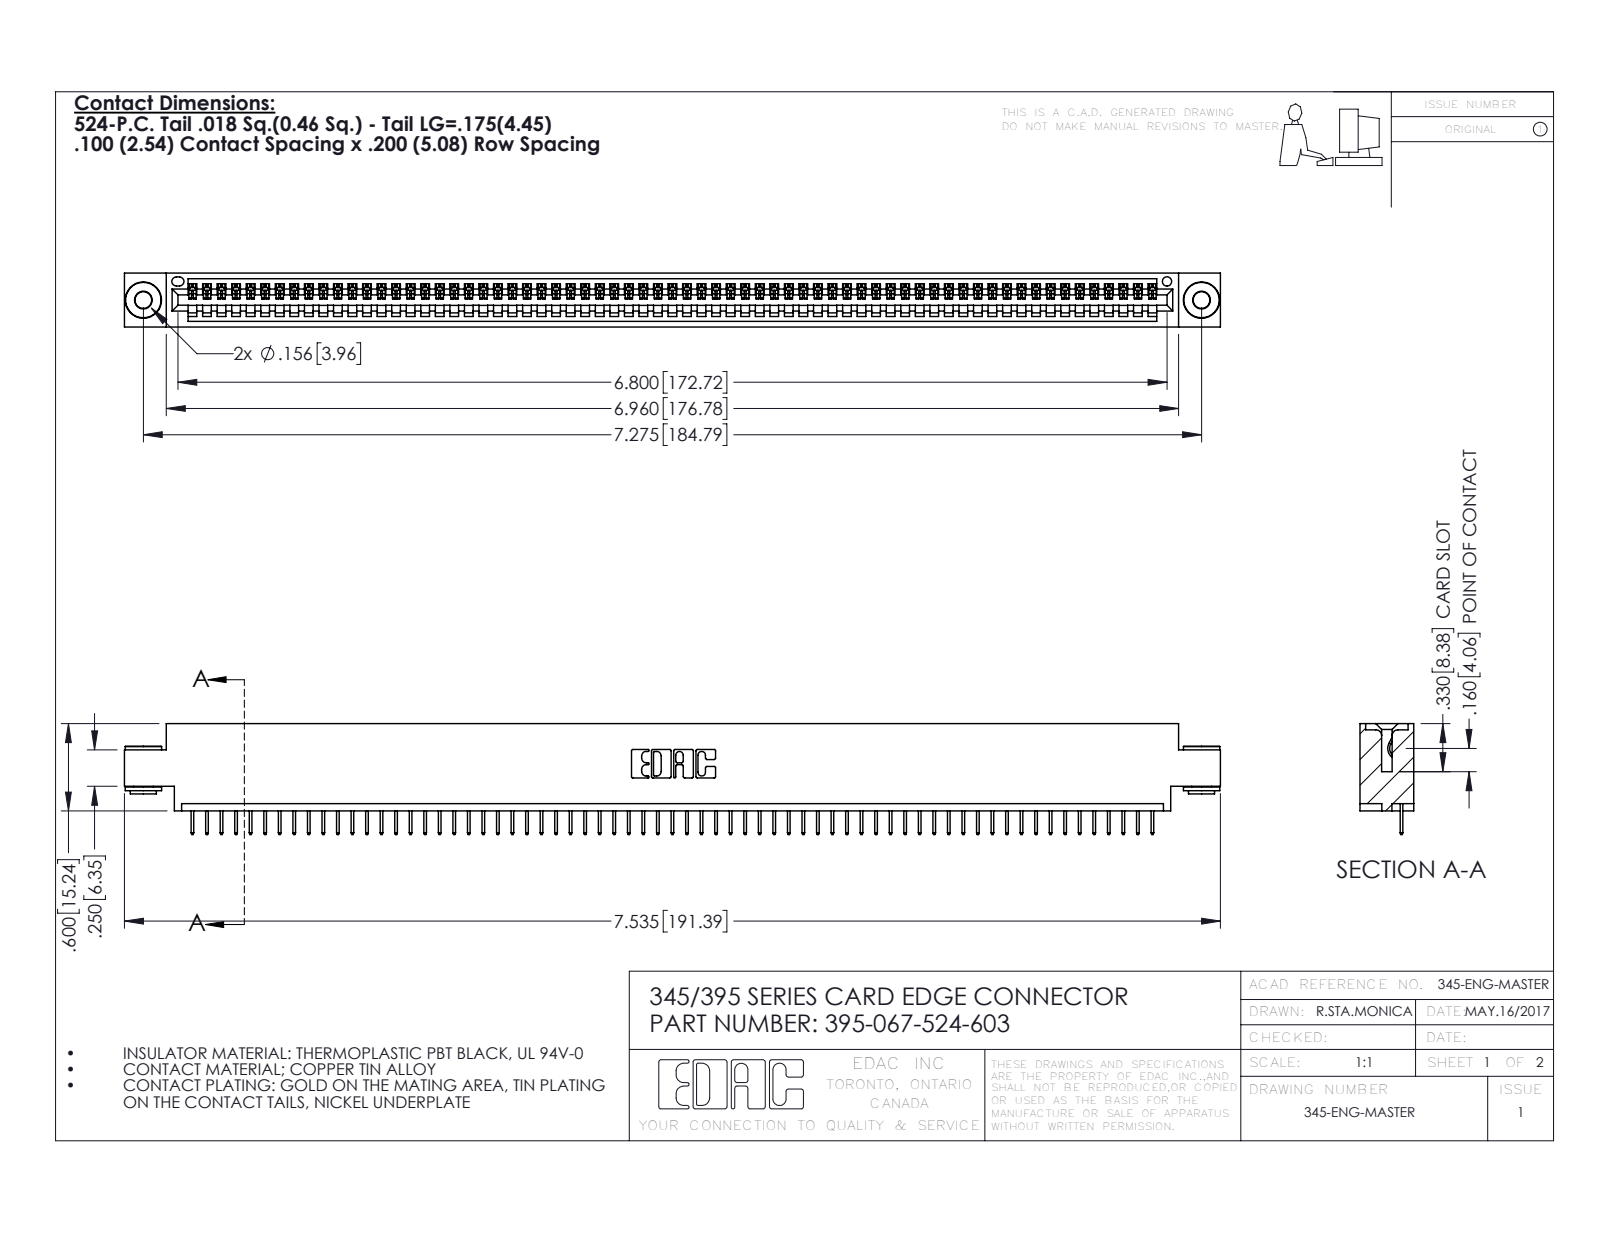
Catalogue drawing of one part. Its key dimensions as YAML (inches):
part_name: "345 Part_0.170 Offset - 0.156 Dia-TH; 345-250-002_345-250-002-102; 345-292-001_345-293-124; 395-067-524-603"
step_written_by: "SolidWorks 2016 (CONFIG_CONTROL_DESIGN)"
units: inches
bodies: {solids: 70, faces: 4322, planar: 3176, cylindrical: 1138, other: 8}
overall_size: [7.535, 0.762, 0.37]
volume: 1.1
surface_area: 36.87
round_holes:
  - {diameter: 0.116, count: 2}
  - {diameter: 0.156, count: 2}
  - {diameter: 0.064, count: 1}
round_bosses_or_shafts:
  - {diameter: 0.25, count: 2}
  - {diameter: 0.18, count: 2}
  - {diameter: 0.136, count: 2}
partial_cylinders:
  - {radius: 0.006, count: 134}
  - {radius: 0.01, count: 22}
  - {radius: 0.007, count: 6}
  - {radius: 0.031, count: 6}
  - {radius: 0.026, count: 3}
  - {radius: 0.031, count: 2}
  - {radius: 0.04, count: 2}
  - {radius: 0.014, count: 1}
face_to_face_distances: [0.072, 0.298, 0.37, 0.2, 0.098, 0.272, 0.025, 0.225, 0.072, 0.175]
hole_center_spacings: [0.27, 7.039, 7.275]
